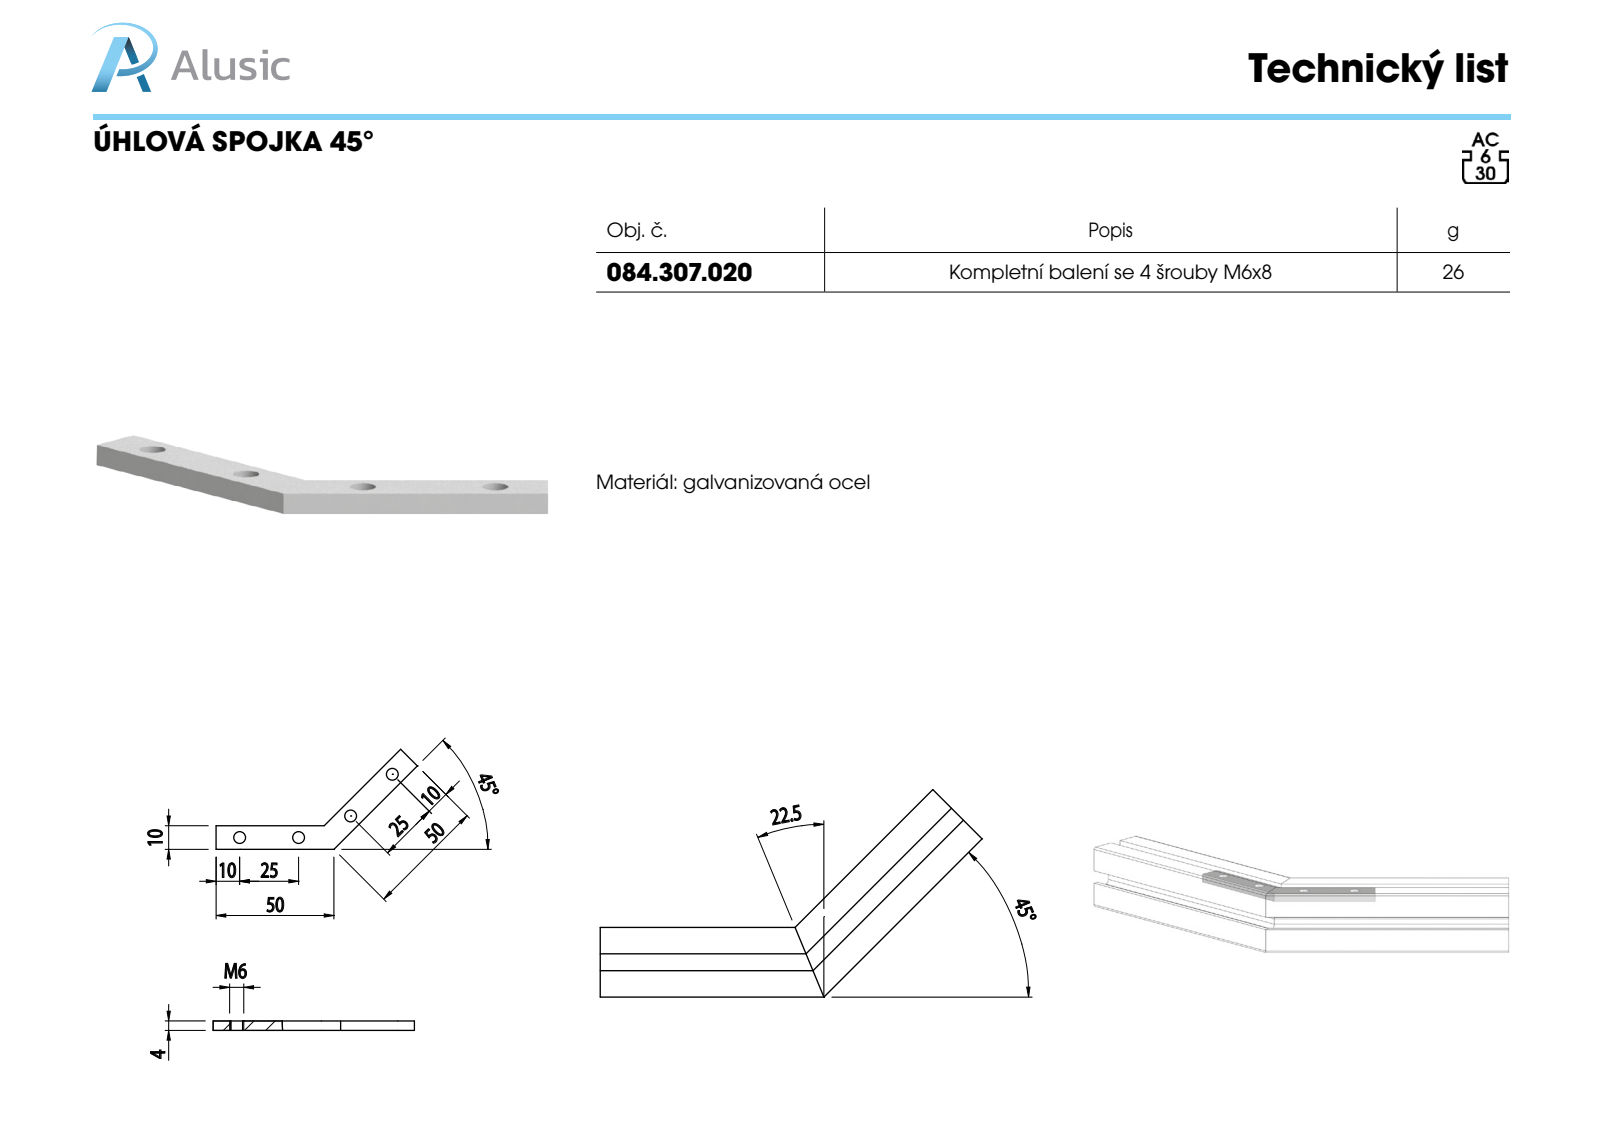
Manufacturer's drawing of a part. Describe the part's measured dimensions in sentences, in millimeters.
The part is named "084.307.020". Its 3-D file was written by "SolidWorks 2011 (CONFIG_CONTROL_DESIGN)". It is 1 solid with 16 faces: 8 planar, 8 cylindrical and 0 other. Overall it measures 85.36 by 42.43 by 4 millimeters. Its volume is 3 520 cubic millimeters and its surface area 2 858 square millimeters. Round holes: 4 of diameter 5. The main face-to-face distances are 4, 10. The hole center spacings are 25, 47.95, 23.89, 70.08.
